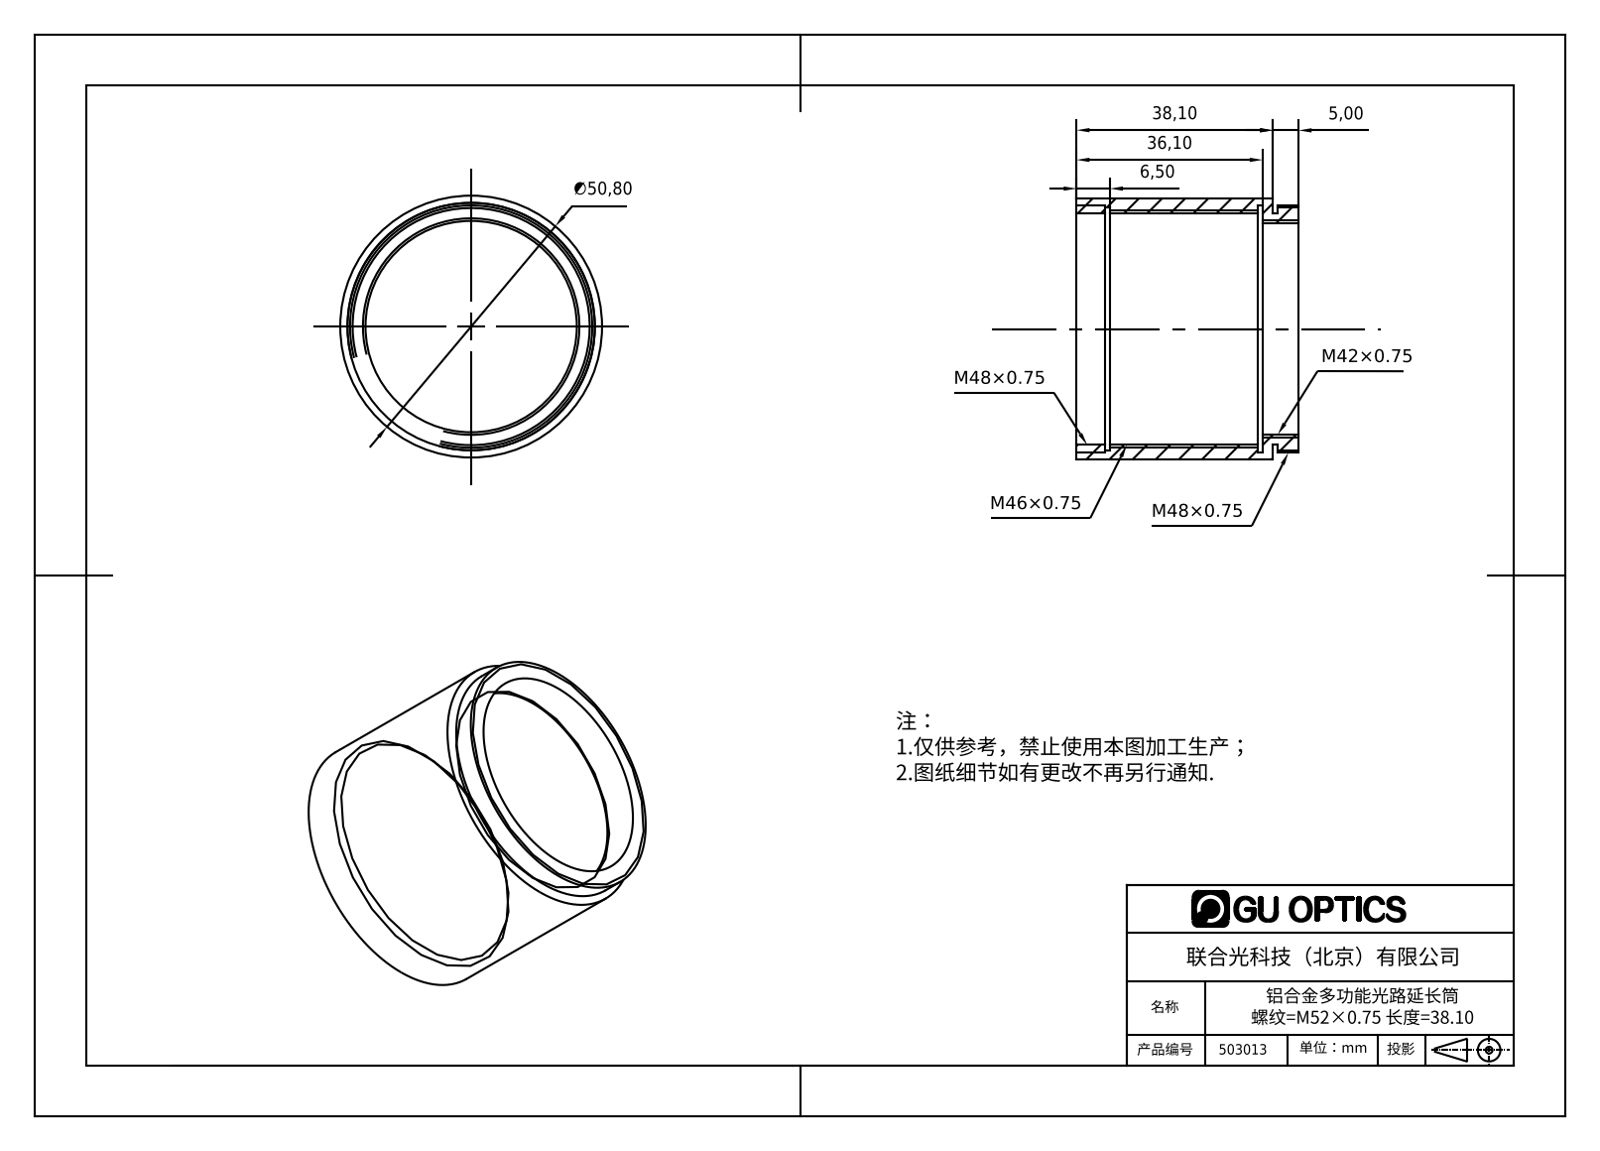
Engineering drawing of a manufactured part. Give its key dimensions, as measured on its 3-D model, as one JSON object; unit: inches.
{"part_name": "503013", "step_written_by": "SolidWorks 2016 (AUTOMOTIVE_DESIGN)", "units": "inches", "bodies": {"solids": 1, "faces": 24, "planar": 8, "cylindrical": 16, "other": 0}, "overall_size": [2, 2, 1.697], "volume_in3": 1.161, "surface_area_in2": 23.91, "round_holes": [[1.614, 1], [1.772, 1], [1.85, 1], [1.89, 1]], "round_bosses_or_shafts": [[2, 1]], "face_to_face_distances": [0.039, 0.276, 0.118, 0.157, 0.079, 0.197, 1.421, 1.5, 1.697, 1.165]}
